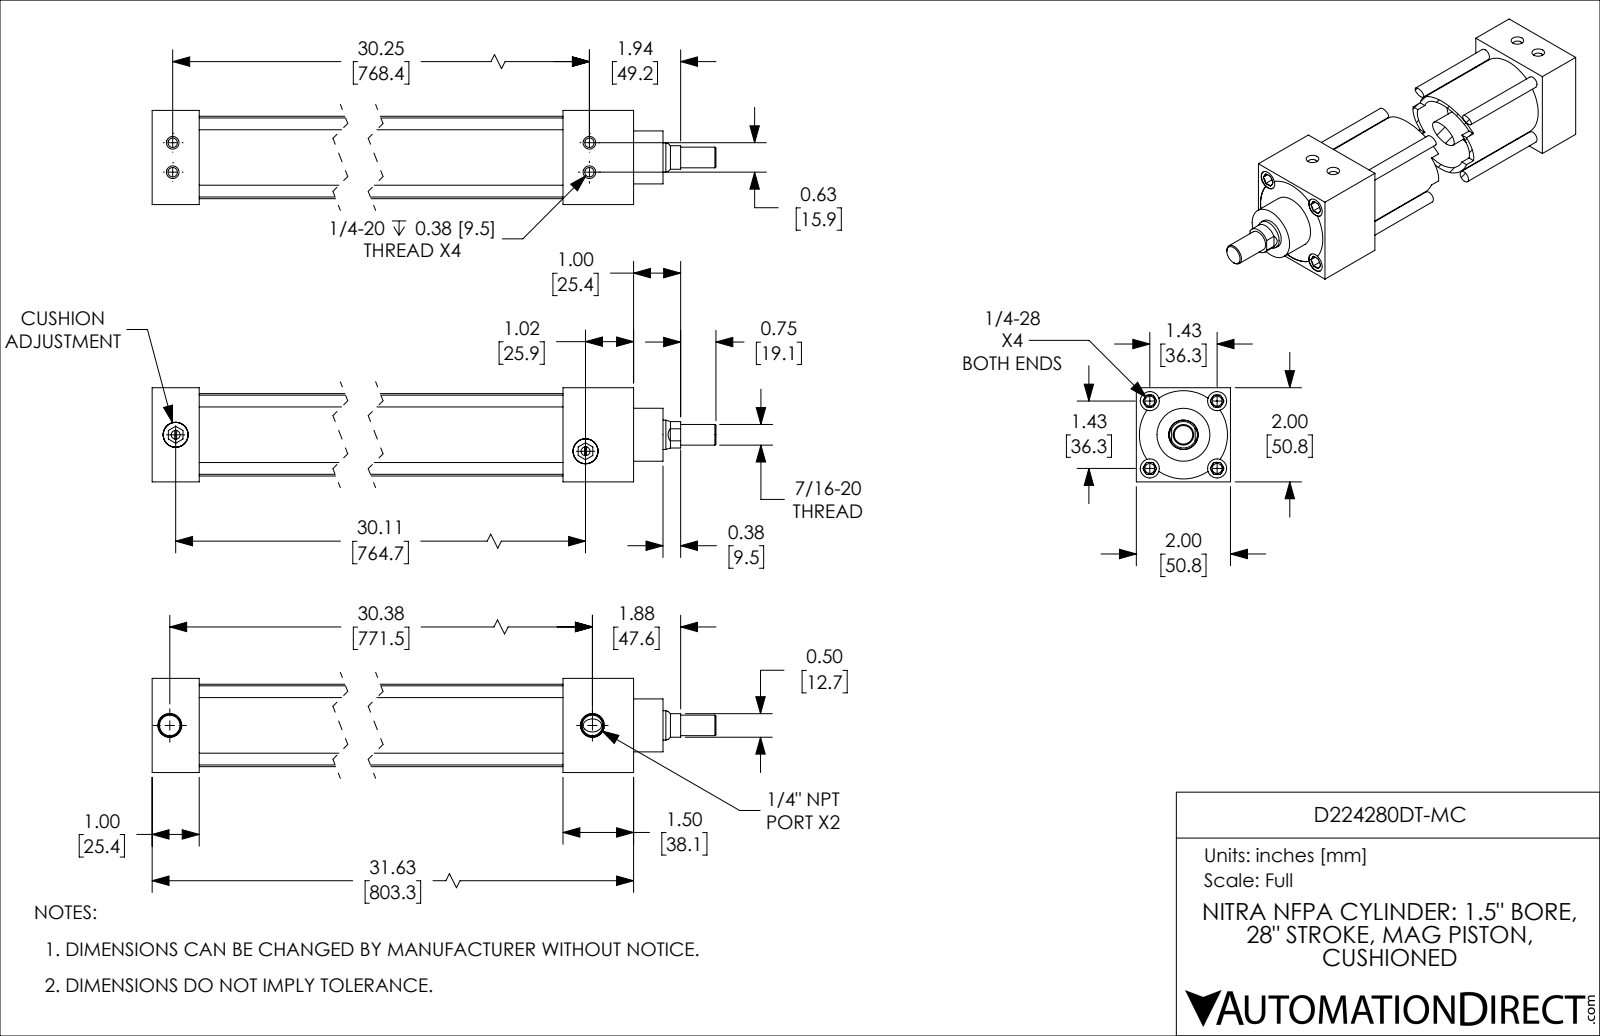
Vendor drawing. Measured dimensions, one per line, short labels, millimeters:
name: D224280DT-MC_BODY; D224280DT-MC_CUSHION; D224280DT-MC_PISTON_KK1; D224280DT-MC
written by: SolidWorks 2019 (CONFIG_CONTROL_DESIGN)
unit: mm
bodies: 4 solids, 251 faces (90 planar, 81 cylindrical, 80 other)
size: 847.7 × 50.8 × 50.8
volume: 739 200 mm³; area: 327 600 mm²
holes: 4× ⌀5.1, 4× ⌀5.4, 4× ⌀10.3, 2× ⌀4.8, 2× ⌀11.1, 2× ⌀13.5, 1× ⌀15.9, 1× ⌀38.1
bosses: 4× ⌀6.4, 2× ⌀13.5, 1× ⌀44.5, 1× ⌀38.1, 1× ⌀28.6, 1× ⌀15.8, 1× ⌀11.1
rounds: 1× R7.1, 1× R23.8
face distances: 50.8, 25.4, 765.2, 739.8, 803.1, 777.7, 38, 28.6, 54, 711.2
hole spacings: 8.1, 25.7, 36.3, 15.9, 51.4, 768.4, 768.5, 770
